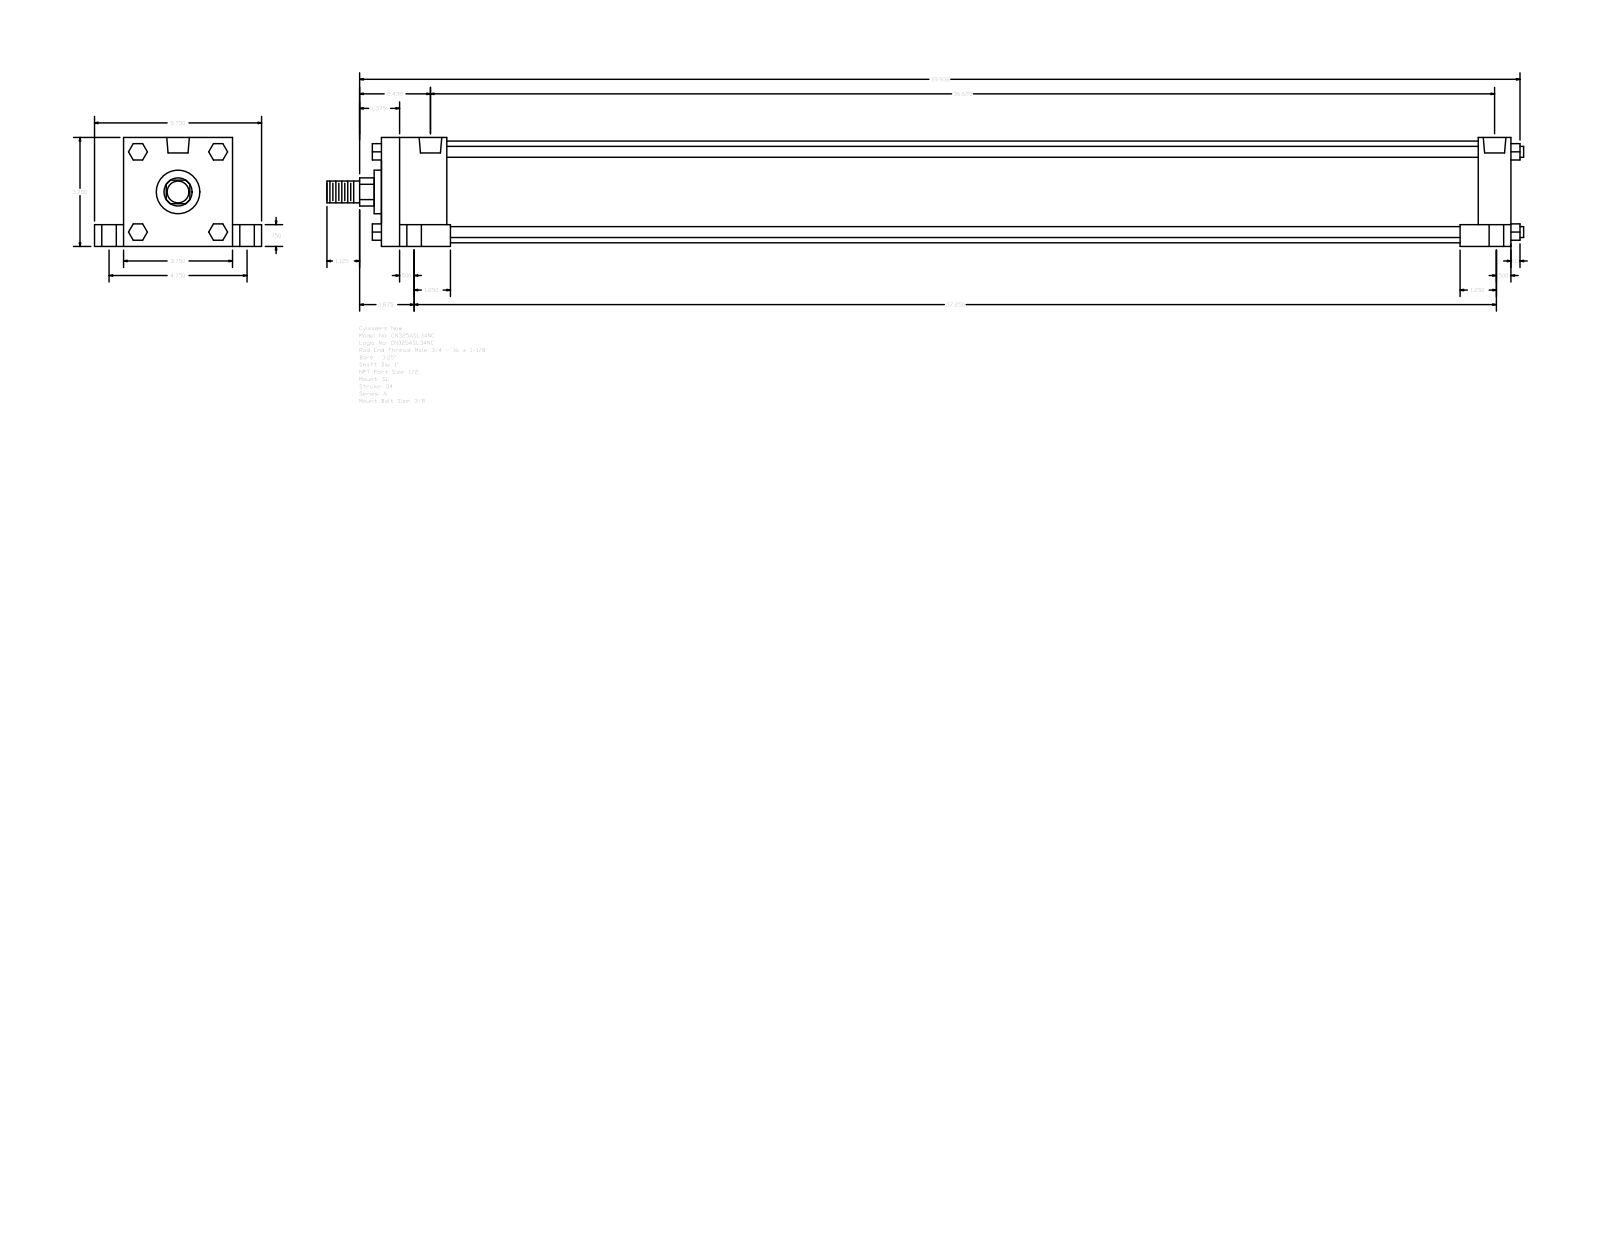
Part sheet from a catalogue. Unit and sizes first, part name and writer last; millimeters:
Units: millimetres
Overall size (bounding box): 1046.16 × 146.05 × 95.25
Round holes (diameter × count): ⌀8.73 ×4, ⌀12.7 ×4, ⌀19.05 ×4, ⌀19.77 ×2
Round bosses / shafts (diameter × count): ⌀9.53 ×4, ⌀88.9 ×1, ⌀38.1 ×1, ⌀25.4 ×1, ⌀19.05 ×1
Partial cylindrical surfaces — rounded edges, fillets, slot ends (radius × count): R12.29 ×1
Main face-to-face distances: 95.24, 987.43, 19.05, 25.41, 120.65, 76.19, 57.15, 958.85, 901.7, 930.28
Hole centre spacings: 3.18, 60.35, 60.52, 62, 62.81, 120.66, 923.92, 927.1
Bodies: 0 solids, 150 faces (114 planar, 36 cylindrical, 0 other)
Part name (STEP PRODUCT): A_SL__0325_1
STEP written by: GSSL Pune (CONFIG_CONTROL_DESIGN)
